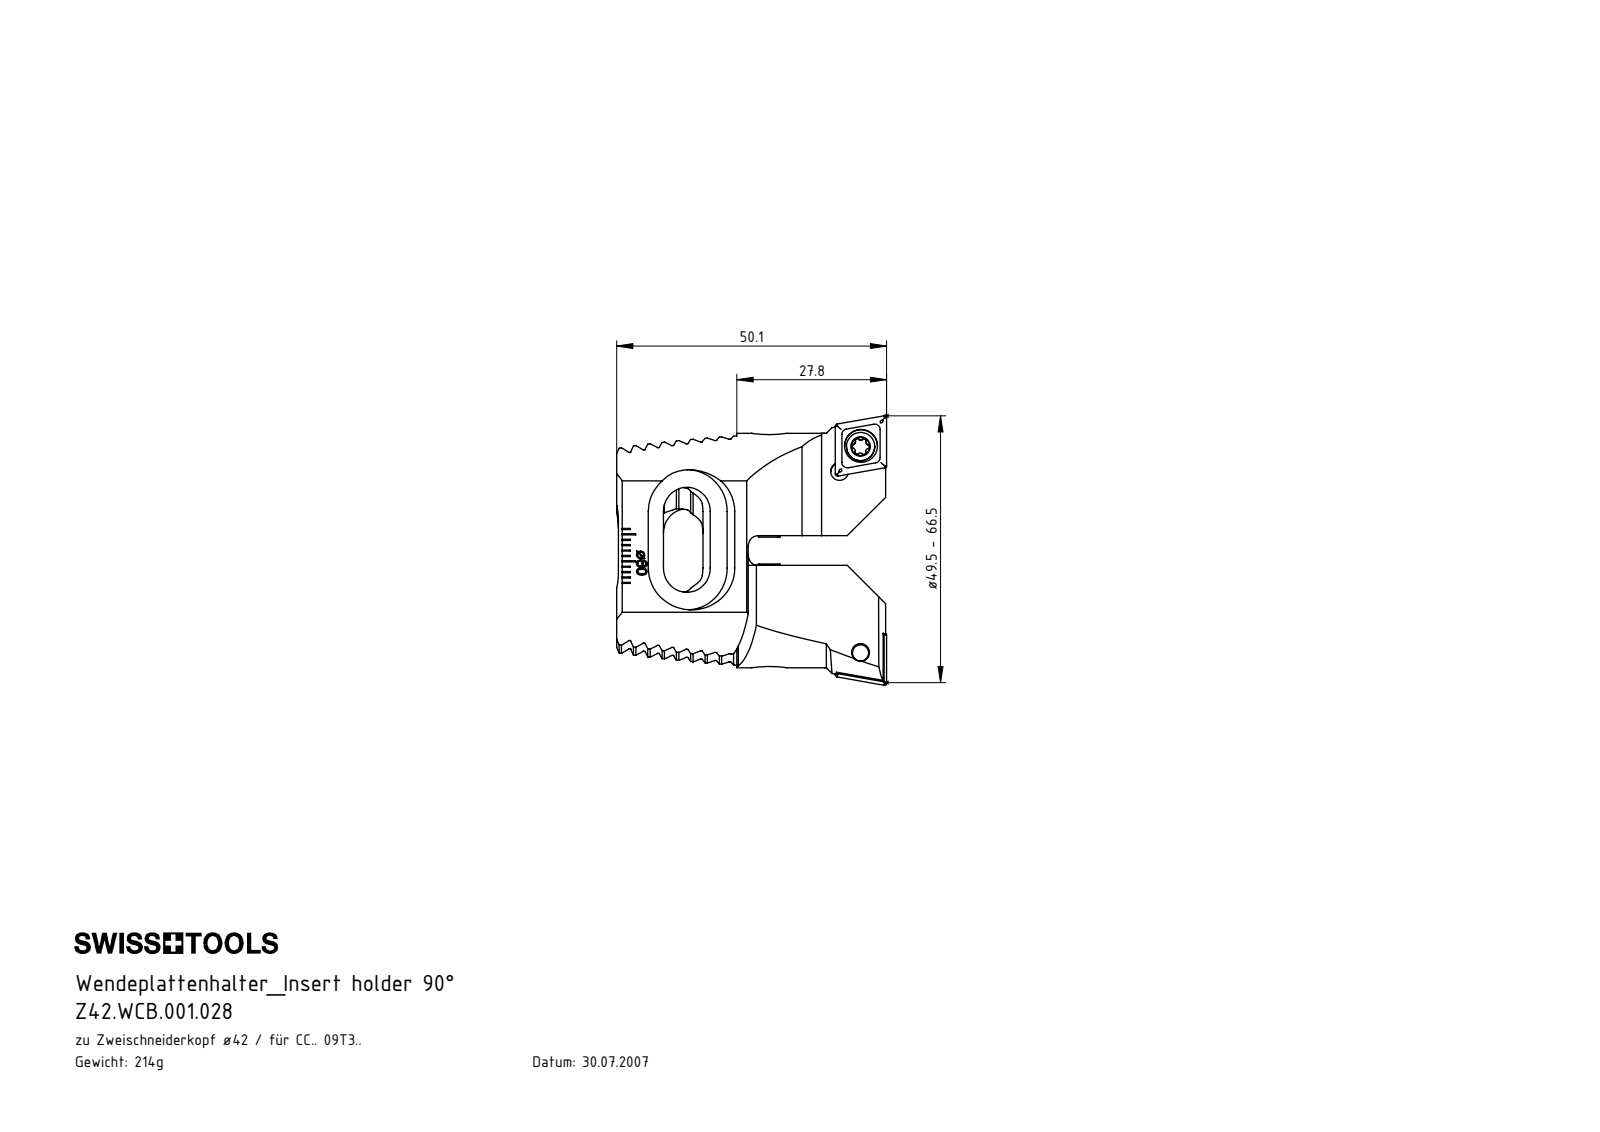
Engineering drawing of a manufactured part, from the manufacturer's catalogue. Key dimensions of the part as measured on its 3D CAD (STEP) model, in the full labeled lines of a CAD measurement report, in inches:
Part name (STEP PRODUCT): Z42.WCB.001.028; CCMT09T304; WCB-ER2.001.009_A; Z42-xxx.001.028_D (+1 more)
STEP written by: SolidWorks 2022 (AUTOMOTIVE_DESIGN)
Units: inches
Bodies: 8 solids, 636 faces (326 planar, 126 cylindrical, 184 other)
Overall size (bounding box): 1.972 × 1.969 × 1.346
Volume: 1.667 in³ · Surface area: 20.91 in²
Round holes (diameter × count): ⌀0.13 ×4, ⌀0.063 ×2, ⌀0.173 ×2, ⌀0.24 ×2, ⌀0.197 ×1
Round bosses / shafts (diameter × count): ⌀0.157 ×3, ⌀0.207 ×2, ⌀0.236 ×1
Partial cylindrical surfaces — rounded edges, fillets, slot ends (radius × count): R0.008 ×16, R0.013 ×12, R0.023 ×12, R0.079 ×4, R0.177 ×4, R0.305 ×4, R0.472 ×4, R0.827 ×4
Main face-to-face distances: 0.094, 0.187, 0.469, 0.375, 0.563, 0.281, 0.188, 0.281, 0.063, 0.228
Hole centre spacings: 0.239, 0.244, 0.472, 1.344, 1.348, 1.522, 0.913, 1.153
